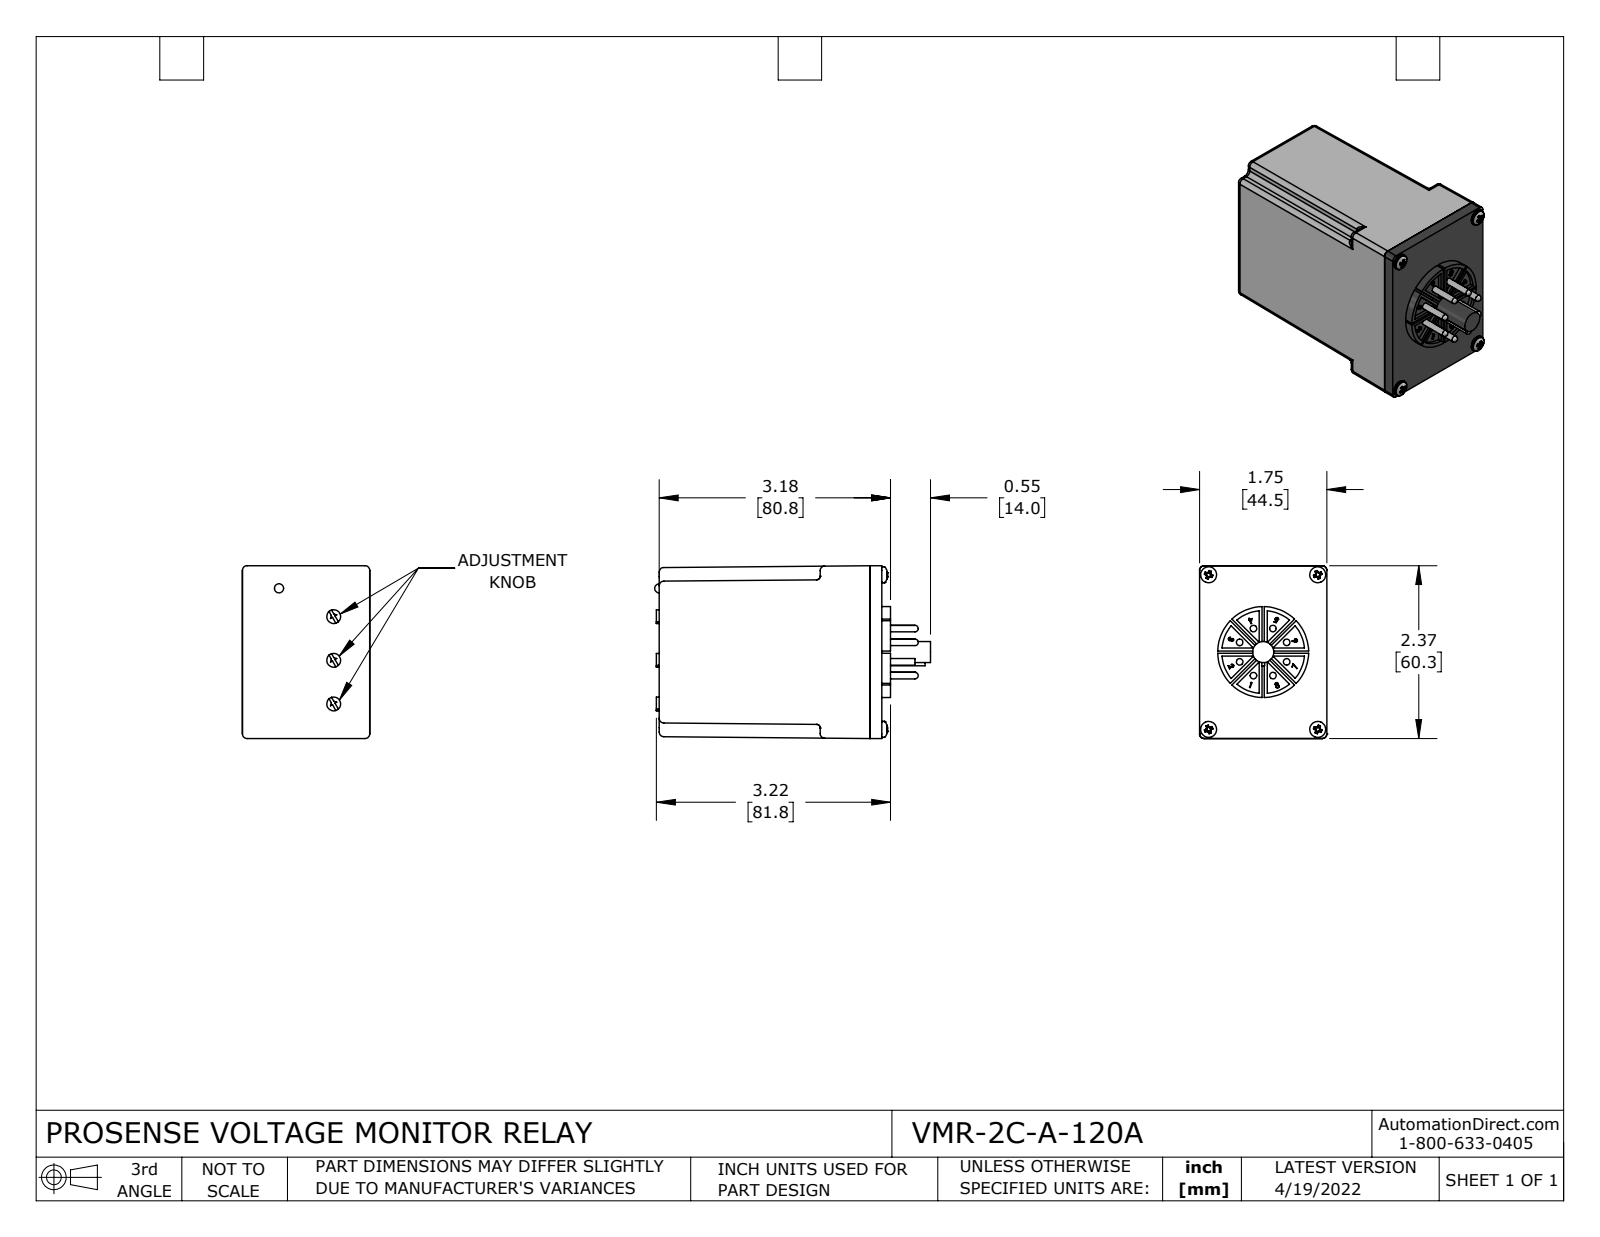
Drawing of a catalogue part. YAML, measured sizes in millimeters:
part_name: "VMR-2C-A-120A"
step_written_by: "SolidWorks 2021 (CONFIG_CONTROL_DESIGN)"
units: millimeters
bodies: {solids: 18, faces: 574, planar: 249, cylindrical: 170, other: 155}
overall_size: [96.3, 60.3, 44.5]
volume: 200700
surface_area: 28850
round_holes:
  - {diameter: 3.2, count: 4}
round_bosses_or_shafts:
  - {diameter: 2.3, count: 8}
  - {diameter: 5.6, count: 4}
  - {diameter: 4.8, count: 3}
  - {diameter: 31.8, count: 1}
  - {diameter: 7.4, count: 1}
partial_cylinders:
  - {radius: 1.6, count: 32}
  - {radius: 0.1, count: 8}
  - {radius: 1.3, count: 4}
  - {radius: 14.5, count: 1}
face_to_face_distances: [73.7, 4.1, 77.7, 1.8, 5.8, 79.5, 4.8, 1.3, 3, 7.1]
hole_center_spacings: [38.1, 54, 66.1]
